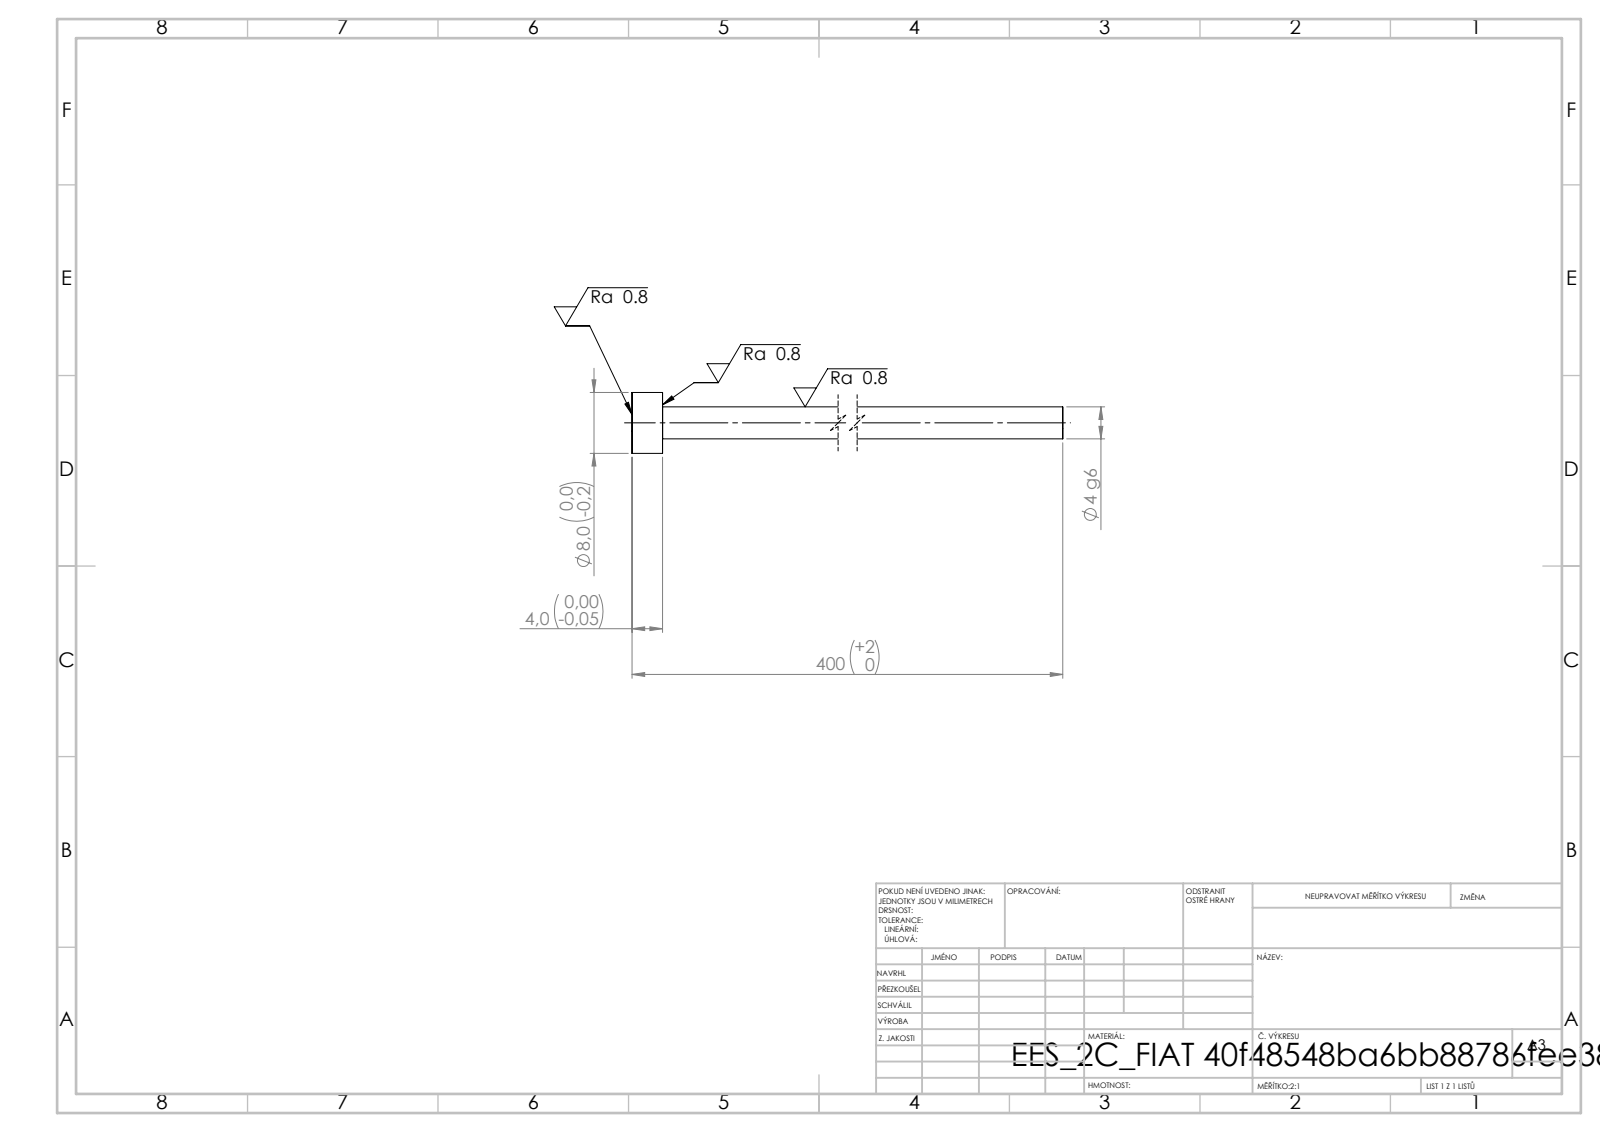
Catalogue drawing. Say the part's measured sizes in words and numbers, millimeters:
Its 3-D file was written by "SolidWorks 2019 (CONFIG_CONTROL_DESIGN)". It is 1 solid with 7 faces: 3 planar, 4 cylindrical and 0 other. Overall it measures 400 by 8 by 8 millimeters. Its volume is 5 687 cubic millimeters and its surface area 5 426 square millimeters. Round bosses or shafts: 1 of diameter 8, 1 of diameter 4.2. The main face-to-face distances are 4, 400, 396.
